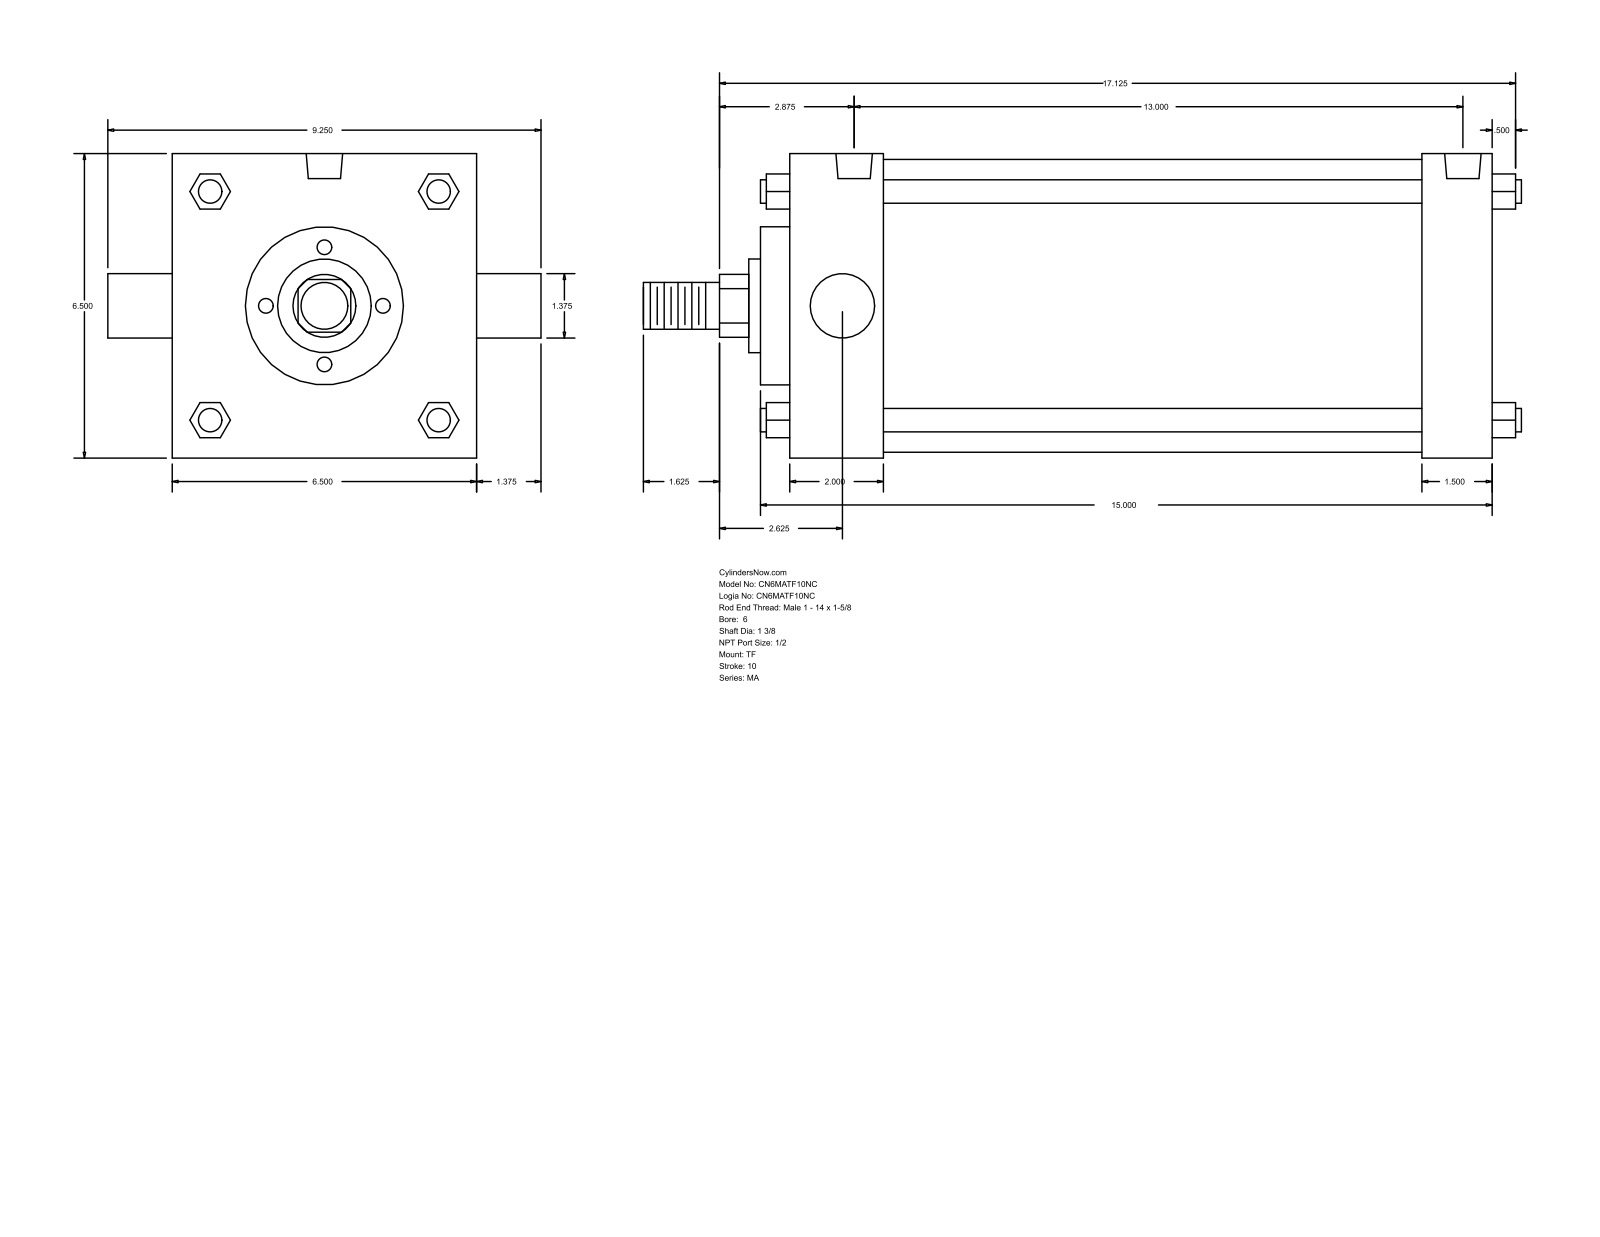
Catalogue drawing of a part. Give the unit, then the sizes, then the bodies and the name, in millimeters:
Units: millimetres
Overall size (bounding box): 476.25 × 234.95 × 165.1
Round holes (diameter × count): ⌀17.46 ×3, ⌀19.77 ×2
Round bosses / shafts (diameter × count): ⌀12.7 ×4, ⌀34.92 ×2, ⌀158.75 ×1, ⌀85.72 ×1, ⌀50.8 ×1, ⌀25.4 ×1
Partial cylindrical surfaces — rounded edges, fillets, slot ends (radius × count): R17.06 ×1
Main face-to-face distances: 165.1, 384.17, 50.8, 346.08, 333.37, 295.28, 38.09, 66.67, 15.87, 361.95
Hole centre spacings: 3.18, 330.2, 333.38
Bodies: 0 solids, 122 faces (93 planar, 29 cylindrical, 0 other)
Part name (STEP PRODUCT): MA_TF__0600_1.375
STEP written by: GSSL Pune (CONFIG_CONTROL_DESIGN)
